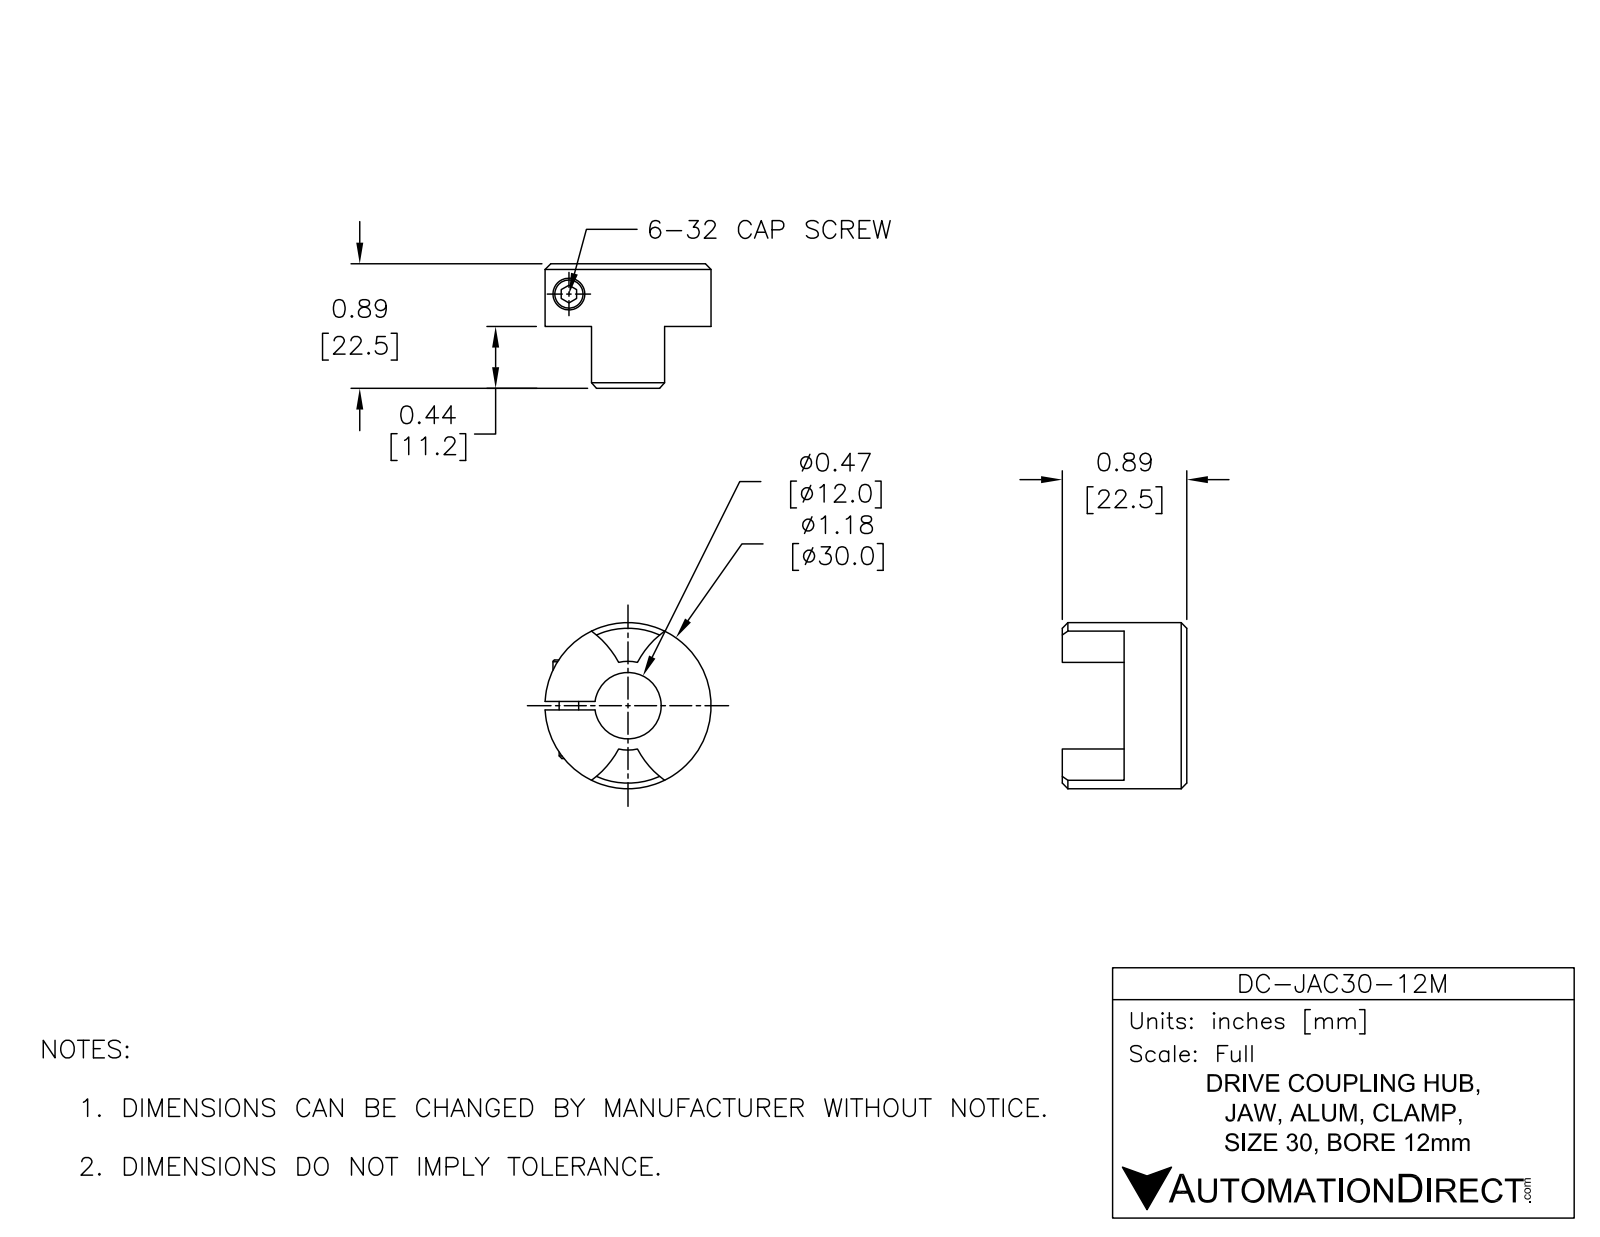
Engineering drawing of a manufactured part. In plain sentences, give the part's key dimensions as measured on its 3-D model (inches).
The part is named "DC-JAC30-12M". Its 3-D file was written by "SolidWorks 2015 (AUTOMOTIVE_DESIGN)". It is 1 solid with 27 faces: 7 planar, 16 cylindrical and 4 other. Overall it measures 1.18 by 1.179 by 0.885 inches. Its volume is 0.451 cubic inches and its surface area 5.673 square inches. Round holes: 1 of diameter 0.154, 1 of diameter 0.25, 1 of diameter 0.472. Round bosses or shafts: 1 of diameter 1.18. Partial cylindrical surfaces (rounded edges, fillets, slot ends): 2 of radius 0.655, 1 of radius 0.315. The main face-to-face distances are 0.445, 0.06, 0.885, 0.44, 0.217, 0.157.
